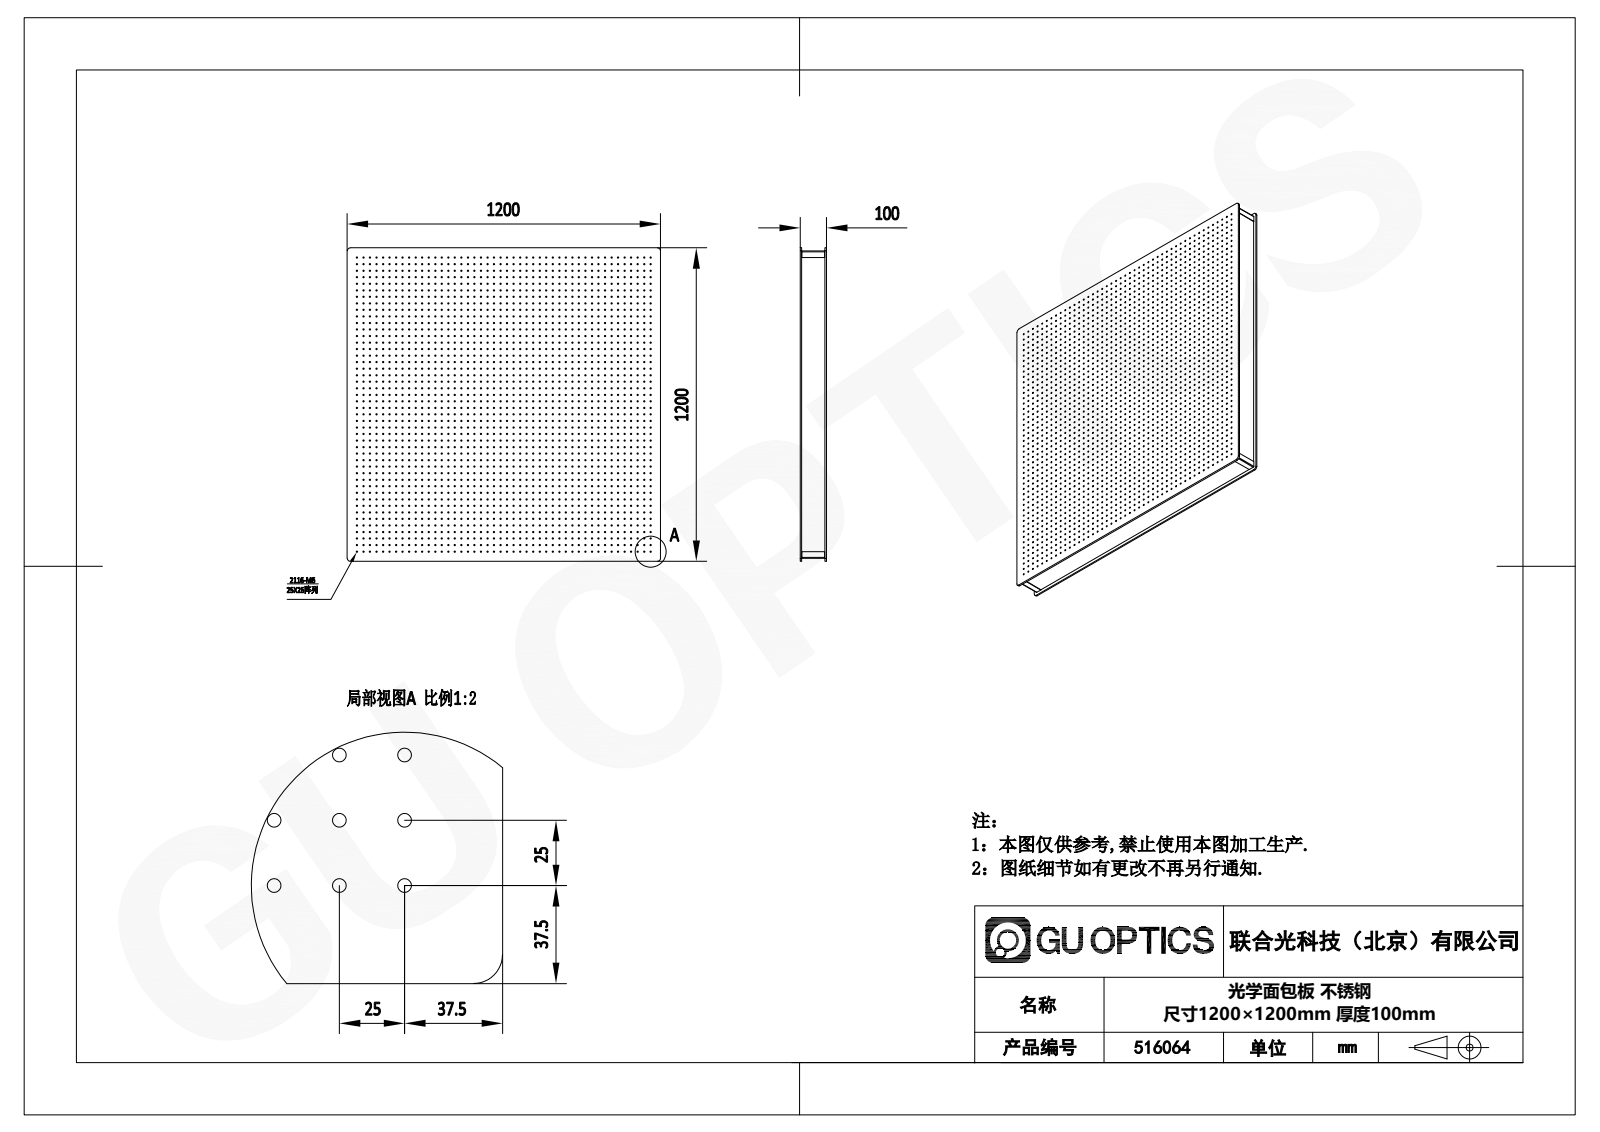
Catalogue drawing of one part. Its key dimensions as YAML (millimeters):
part_name: "516064"
step_written_by: "SolidWorks 2020 (CONFIG_CONTROL_DESIGN)"
units: millimeters
bodies: {solids: 1, faces: 6408, planar: 2160, cylindrical: 4248, other: 0}
overall_size: [1200, 1200, 100]
volume: 138200000
surface_area: 3703000
round_holes:
  - {diameter: 5.3, count: 2116}
partial_cylinders:
  - {radius: 2, count: 4}
  - {radius: 3, count: 4}
  - {radius: 11, count: 4}
face_to_face_distances: [100, 1174, 6, 94, 95, 89, 5, 13, 1187, 1200]
hole_center_spacings: [79.06, 35.36, 50, 127.48, 70.71, 176.78, 111.8, 100]
